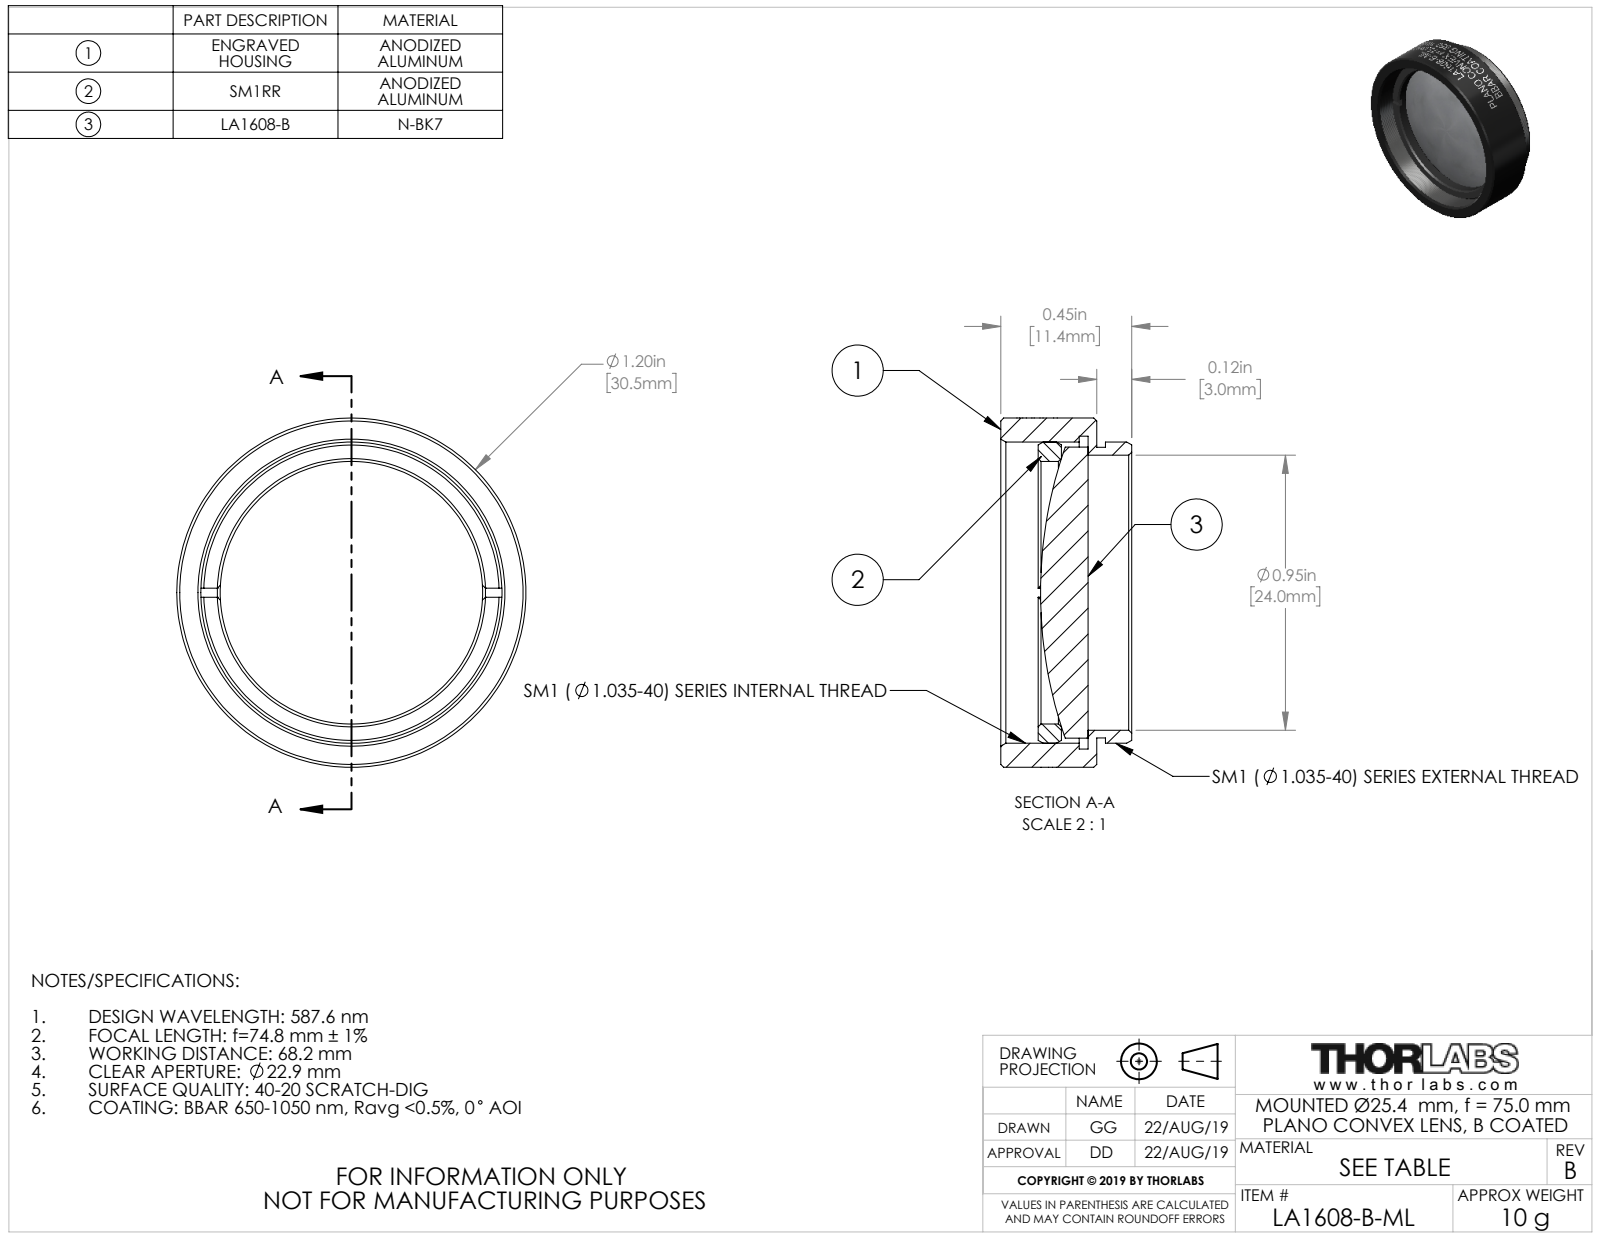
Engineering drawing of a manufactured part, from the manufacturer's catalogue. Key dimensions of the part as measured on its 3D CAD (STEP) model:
Part name (STEP PRODUCT): 24428-E0W
STEP written by: SolidWorks 2018 (CONFIG_CONTROL_DESIGN)
Units: millimetres
Bodies: 3 solids, 155 faces (20 planar, 111 cylindrical, 24 other)
Overall size (bounding box): 30.48 × 30.48 × 11.43
Volume: 3 640 mm³ · Surface area: 4 326 mm²
Round holes (diameter × count): ⌀22.91 ×1, ⌀24 ×1, ⌀26.29 ×1, ⌀27.3 ×1
Round bosses / shafts (diameter × count): ⌀30.48 ×1, ⌀26.29 ×1, ⌀25.4 ×1, ⌀25.37 ×1
Main face-to-face distances: 0.76, 8.38, 7.62, 3.08, 2.32, 5.3, 5.11, 4.35, 2.03, 3.27
